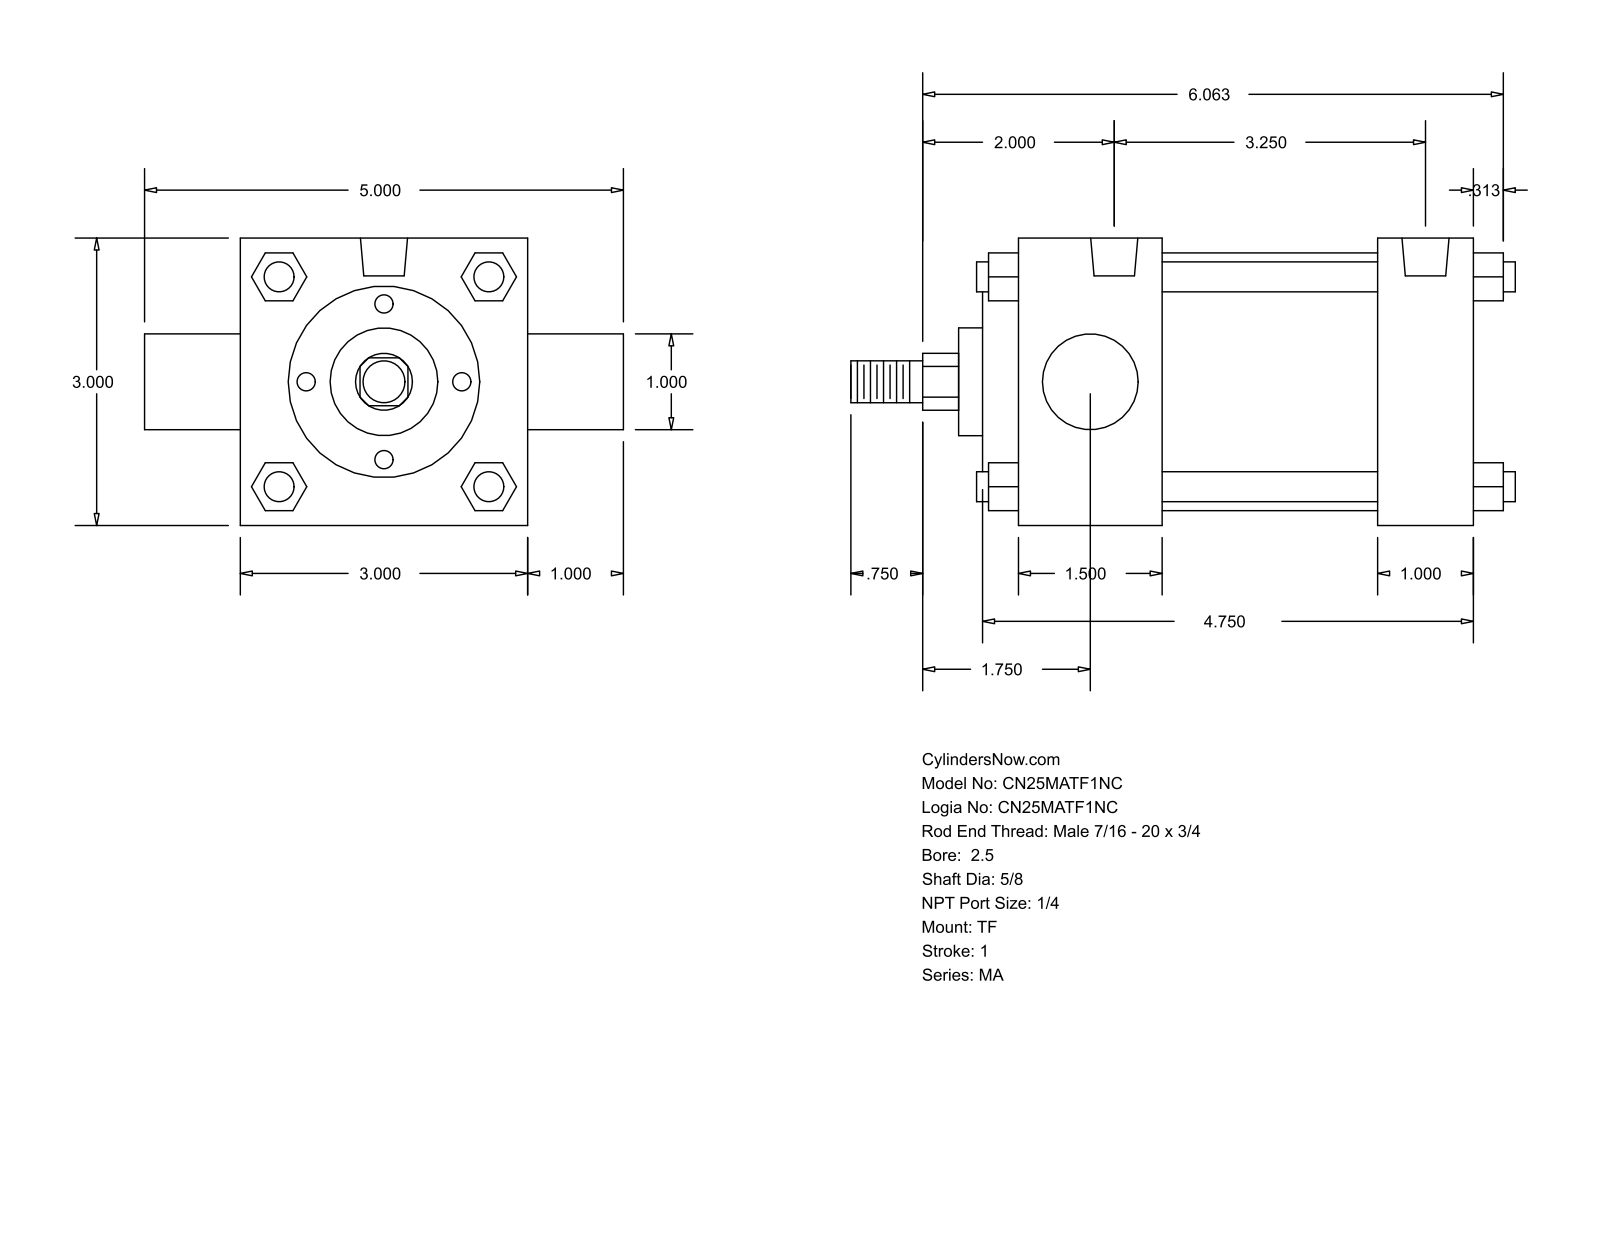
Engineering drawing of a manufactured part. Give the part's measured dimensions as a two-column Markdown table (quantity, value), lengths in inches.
| quantity | value |
| --- | --- |
| part name | MA_TF__0250_0.625 |
| STEP written by | GSSL Pune (CONFIG_CONTROL_DESIGN) |
| units | inches |
| bodies | 0 solids, 122 faces (93 planar, 29 cylindrical, 0 other) |
| overall size | 6.937 × 5 × 3 |
| round holes (diameter × count) | 0.313 × 3, 0.492 × 2 |
| round bosses / shafts (diameter × count) | 0.313 × 4, 2.69 × 1, 2 × 1, 1.125 × 1, 1 × 1, 0.625 × 1, 0.437 × 1 |
| partial cylindrical surfaces (radius × count) | 0.297 × 1 |
| main face-to-face distances | 3, 4.75, 1, 2.25, 3.25, 1.5, 3.75, 0.5, 0.375, 1.875 |
| hole center spacings | 3.25 |
